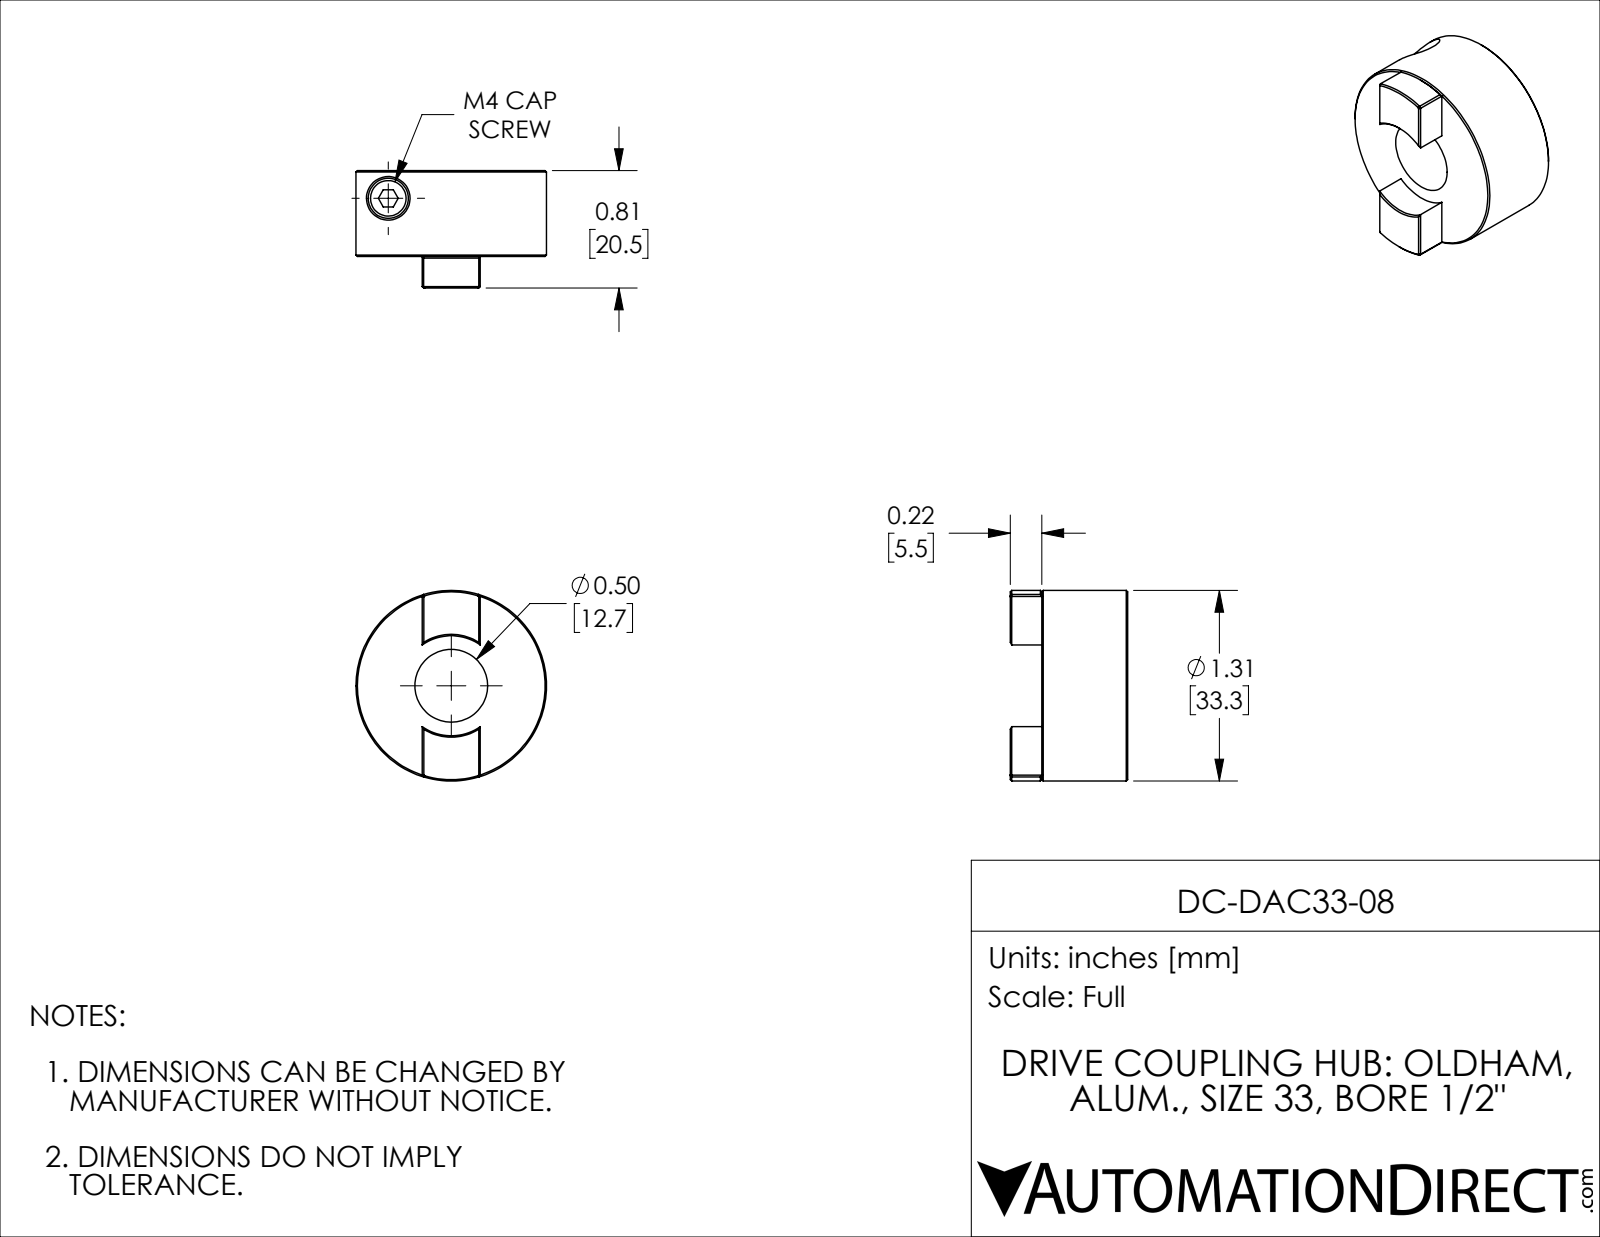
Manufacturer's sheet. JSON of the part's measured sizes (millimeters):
{"part_name": "DC-DAC33-08", "step_written_by": "SolidWorks 2021 (CONFIG_CONTROL_DESIGN)", "units": "millimeters", "bodies": {"solids": 2, "faces": 70, "planar": 36, "cylindrical": 19, "other": 15}, "overall_size": [33.27, 33.27, 20.5], "volume_mm3": 11507, "surface_area_mm2": 4914, "round_holes": [[4.5, 1], [7.62, 1], [12.7, 1]], "round_bosses_or_shafts": [[33.27, 1], [7, 1], [3.9, 1]], "partial_cylinders_radius": [[8.73, 1], [25.4, 1]], "face_to_face_distances": [15, 20.5, 5.5, 10.1, 1.17, 5.72, 4.55, 2.39, 1.22, 3.33]}
